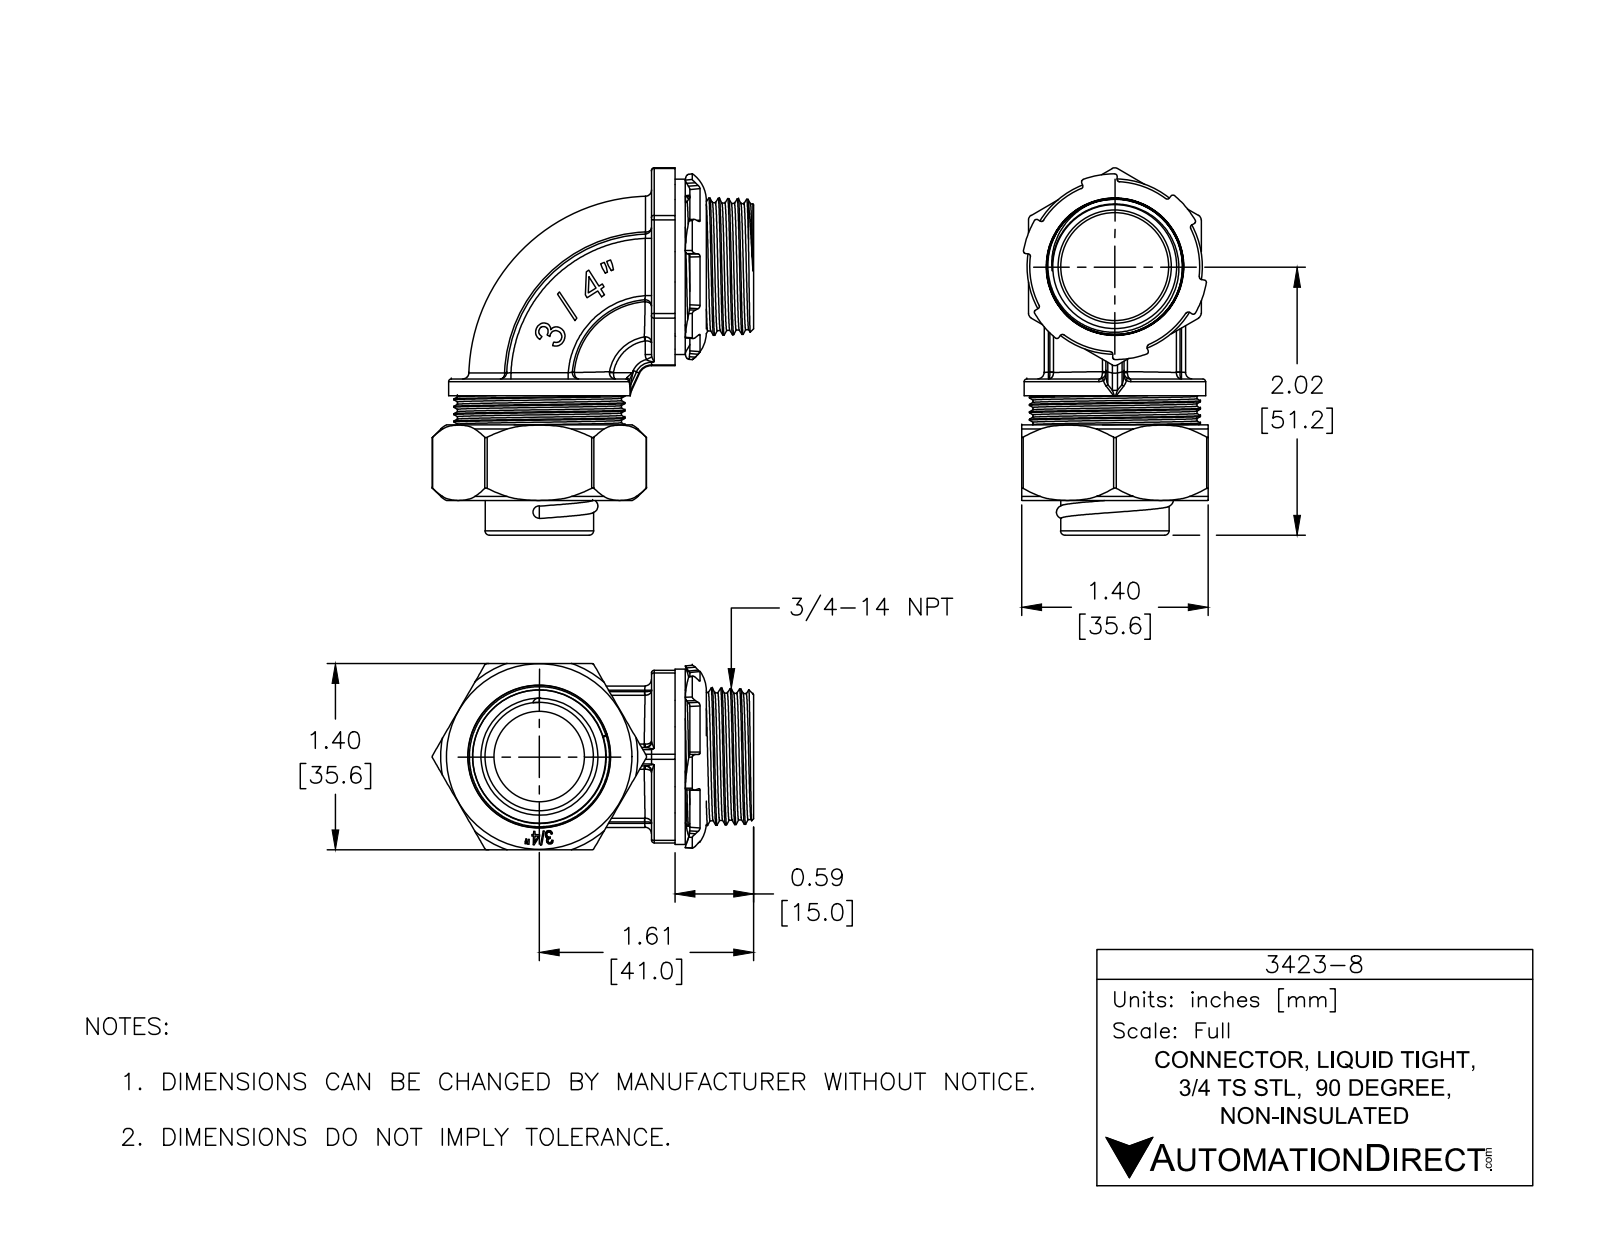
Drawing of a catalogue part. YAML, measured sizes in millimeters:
part_name: "3403 SEAL; 3403 COMPRESSION NUT; 3423 90DEG BODY; 3403 GLAND RING (+3 more)"
step_written_by: "SolidWorks 2014 (AUTOMOTIVE_DESIGN)"
units: millimeters
bodies: {solids: 6, faces: 689, planar: 256, cylindrical: 144, other: 289}
overall_size: [70.2, 61.4, 35.6]
volume: 24450
surface_area: 28200
round_holes:
  - {diameter: 22, count: 2}
  - {diameter: 3.2, count: 1}
  - {diameter: 17.3, count: 1}
  - {diameter: 19.1, count: 1}
  - {diameter: 20.6, count: 1}
  - {diameter: 23, count: 1}
  - {diameter: 26.3, count: 1}
  - {diameter: 27.1, count: 1}
  - {diameter: 27.3, count: 1}
  - {diameter: 28.4, count: 1}
  - {diameter: 31.9, count: 1}
  - {diameter: 33.3, count: 1}
round_bosses_or_shafts:
  - {diameter: 34.7, count: 1}
  - {diameter: 33.5, count: 1}
  - {diameter: 32.7, count: 1}
  - {diameter: 30.8, count: 1}
  - {diameter: 28, count: 1}
  - {diameter: 20.7, count: 1}
  - {diameter: 19, count: 1}
  - {diameter: 2.6, count: 1}
partial_cylinders:
  - {radius: 0.5, count: 12}
  - {radius: 1.2, count: 12}
  - {radius: 0.2, count: 8}
  - {radius: 1, count: 7}
  - {radius: 0.8, count: 2}
  - {radius: 0.1, count: 1}
  - {radius: 0.3, count: 1}
  - {radius: 0.4, count: 1}
face_to_face_distances: [4.3, 31.3, 35.6, 20, 27, 2, 35.6, 23.2, 3.2, 6.5]
hole_center_spacings: [15.6]
